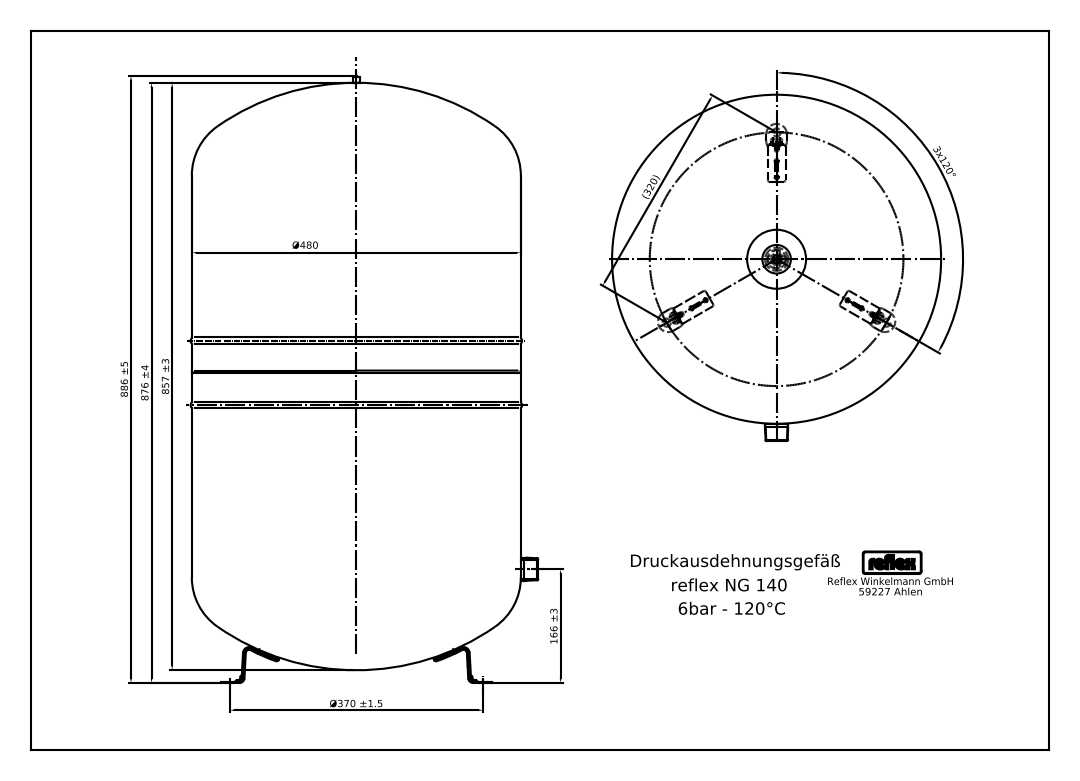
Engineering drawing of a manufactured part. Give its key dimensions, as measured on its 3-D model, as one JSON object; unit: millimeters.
{"step_written_by": "Mechanical Desktop 2011 (CONFIG_CONTROL_DESIGN)", "units": "millimeters", "bodies": {"solids": 16, "faces": 191, "planar": 76, "cylindrical": 74, "other": 41}, "overall_size": [912, 521, 512], "volume_mm3": 143500000, "surface_area_mm2": 2312000, "round_holes": [[15, 3], [25.7, 1]], "round_bosses_or_shafts": [[512, 1], [480, 1], [33.7, 1], [10, 1], [6, 1]], "partial_cylinders_radius": [[148.38, 9], [150.38, 9], [15, 6], [2.81, 4], [1.12, 3], [1.92, 2], [3.38, 2], [4.64, 2]], "face_to_face_distances": [622, 300.25, 321.75, 21.5, 449.25, 149, 470.75, 771, 2, 147], "hole_center_spacings": [320.43, 320.42]}
